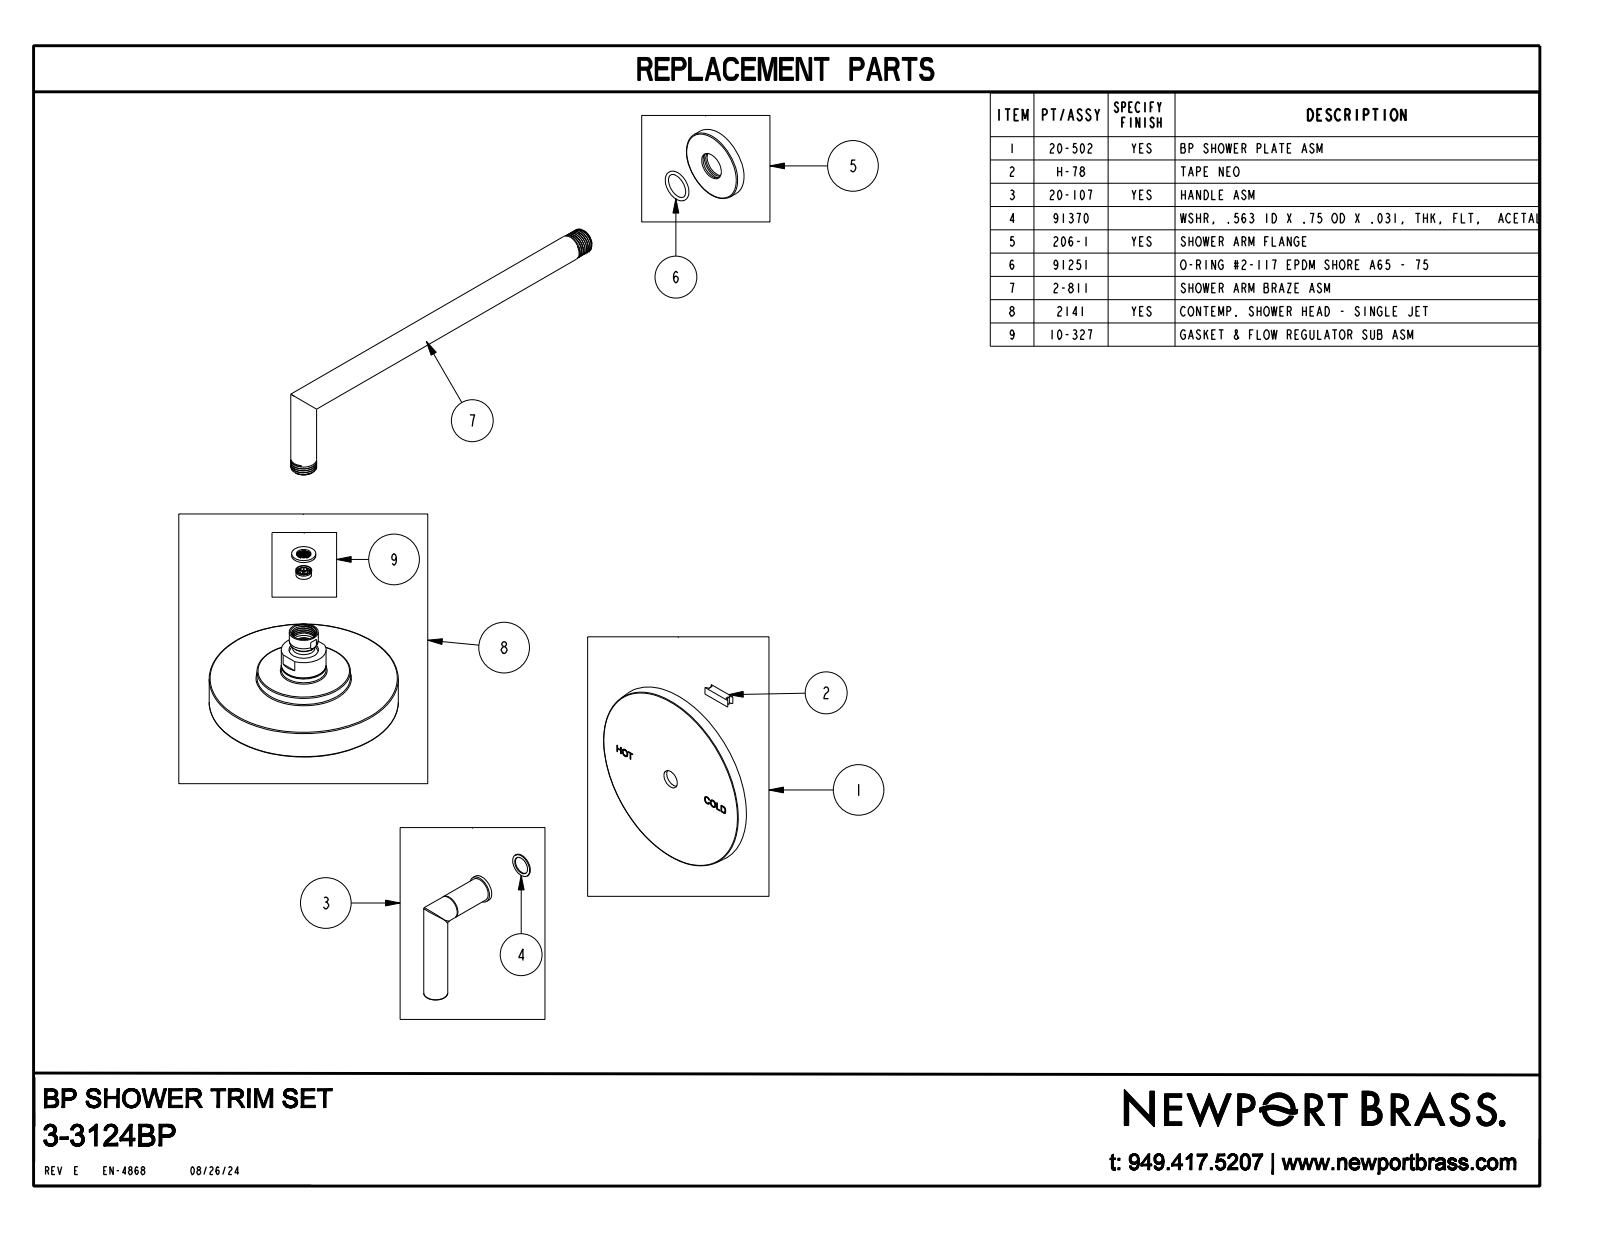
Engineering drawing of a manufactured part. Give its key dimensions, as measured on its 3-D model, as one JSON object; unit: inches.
{"part_name": "3-3124BP", "step_written_by": "CREO PARAMETRIC BY PTC INC, 2018400 (CONFIG_CONTROL_DESIGN)", "units": "inches", "bodies": {"solids": 2, "faces": 992, "planar": 158, "cylindrical": 214, "other": 620}, "overall_size": [16.125, 14.605, 6], "volume_in3": 54.67, "surface_area_in2": 206.9, "round_holes": [[0.05, 90], [0.22, 1], [5.256, 1]], "round_bosses_or_shafts": [[0.813, 2], [0.75, 2], [5.91, 1], [5.22, 1], [2.92, 1], [2.25, 1], [1.4, 1], [0.905, 1]], "face_to_face_distances": [0.35, 0.291, 0.31, 0.04, 1.084, 0.793, 10.972, 11.263, 12.056, 0.031], "hole_center_spacings": [0.851, 0.98, 0.98, 1.698, 1.41, 0.55, 0.507, 0.574]}
